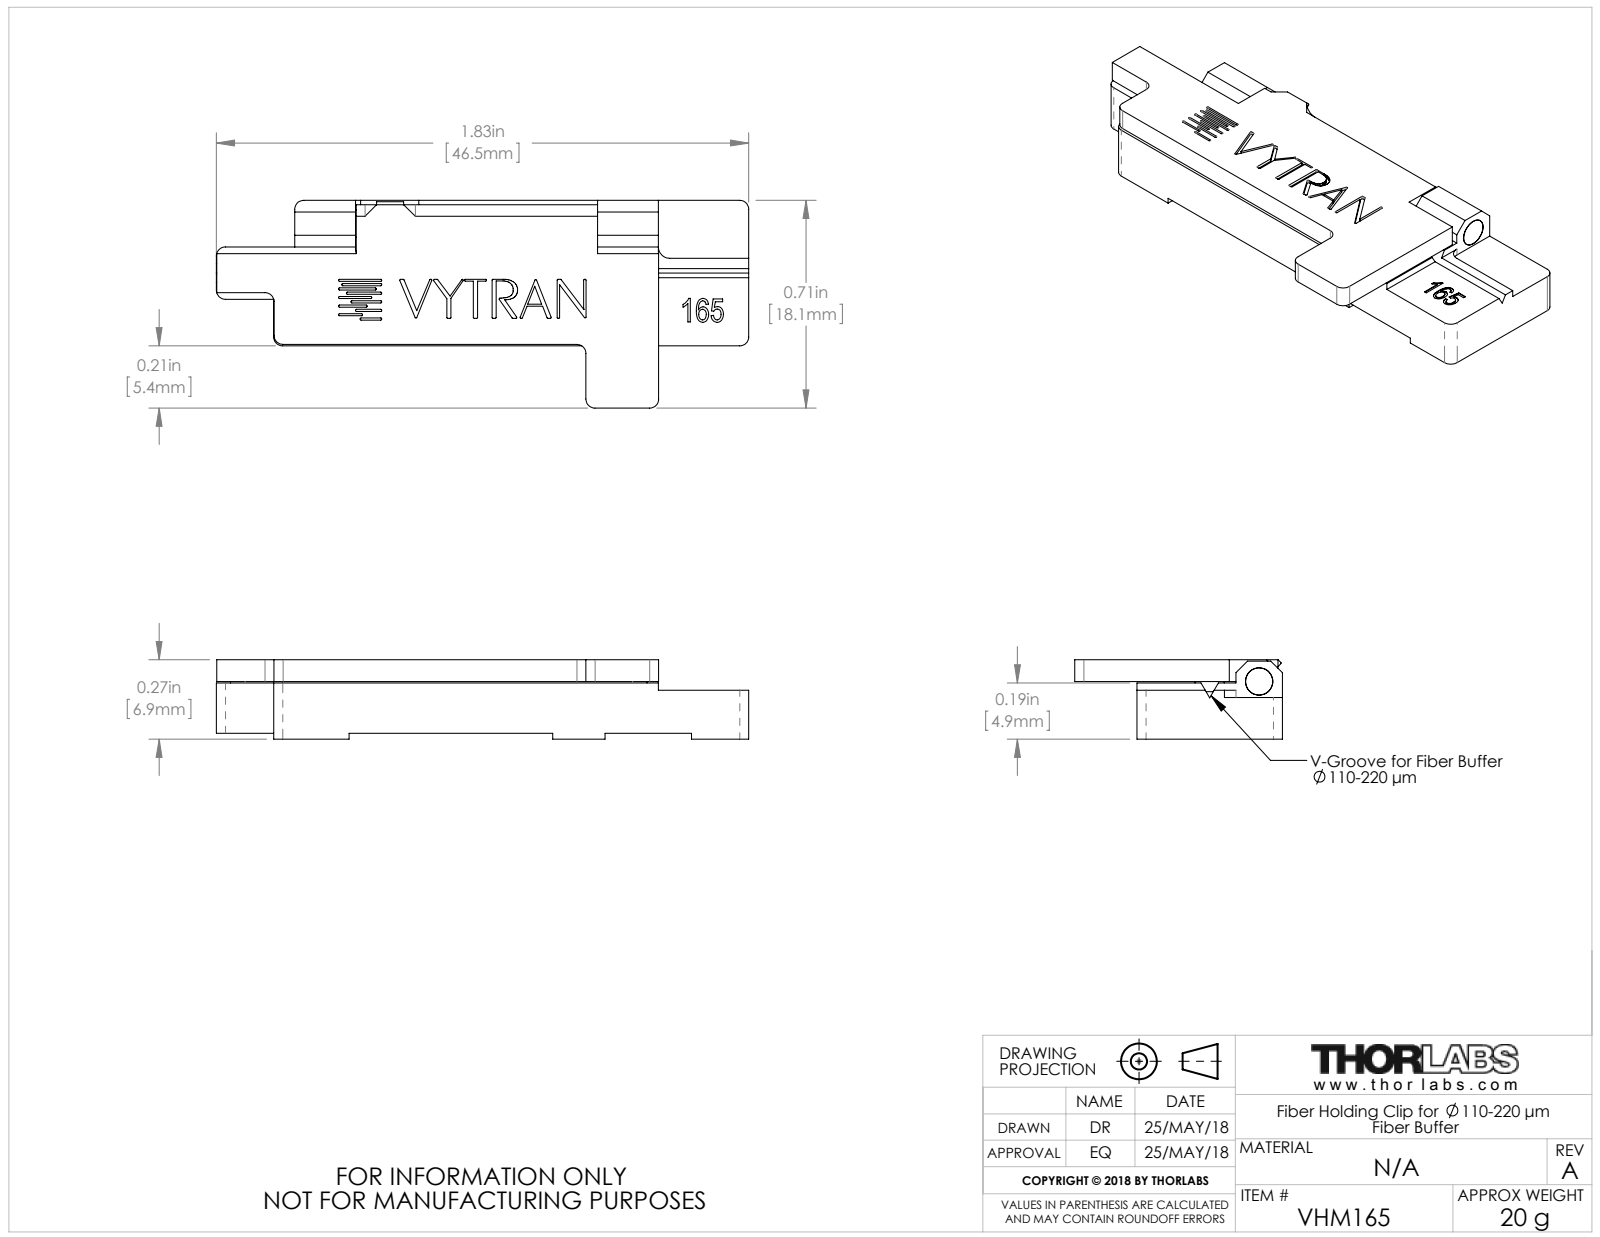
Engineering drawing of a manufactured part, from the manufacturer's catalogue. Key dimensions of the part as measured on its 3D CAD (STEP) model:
Part name (STEP PRODUCT): TTN048005-E0W
STEP written by: SolidWorks 2014 (CONFIG_CONTROL_DESIGN)
Units: inches
Bodies: 0 solids, 351 faces (216 planar, 108 cylindrical, 27 other)
Overall size (bounding box): 1.83 × 0.714 × 0.273
Round holes (diameter × count): ⌀0.123 ×5, ⌀0.094 ×1, ⌀0.126 ×1, ⌀0.21 ×1
Partial cylindrical surfaces — rounded edges, fillets, slot ends (radius × count): R0.031 ×7, R0.031 ×4, R0.039 ×4
Main face-to-face distances: 0.253, 0.178, 0.075, 0.02, 0.198, 0.273, 0.173, 0.193, 0.08, 0.5
Hole centre spacings: 0.489, 0.965, 1.164, 1.441, 0.2, 0.278, 0.32, 0.551
